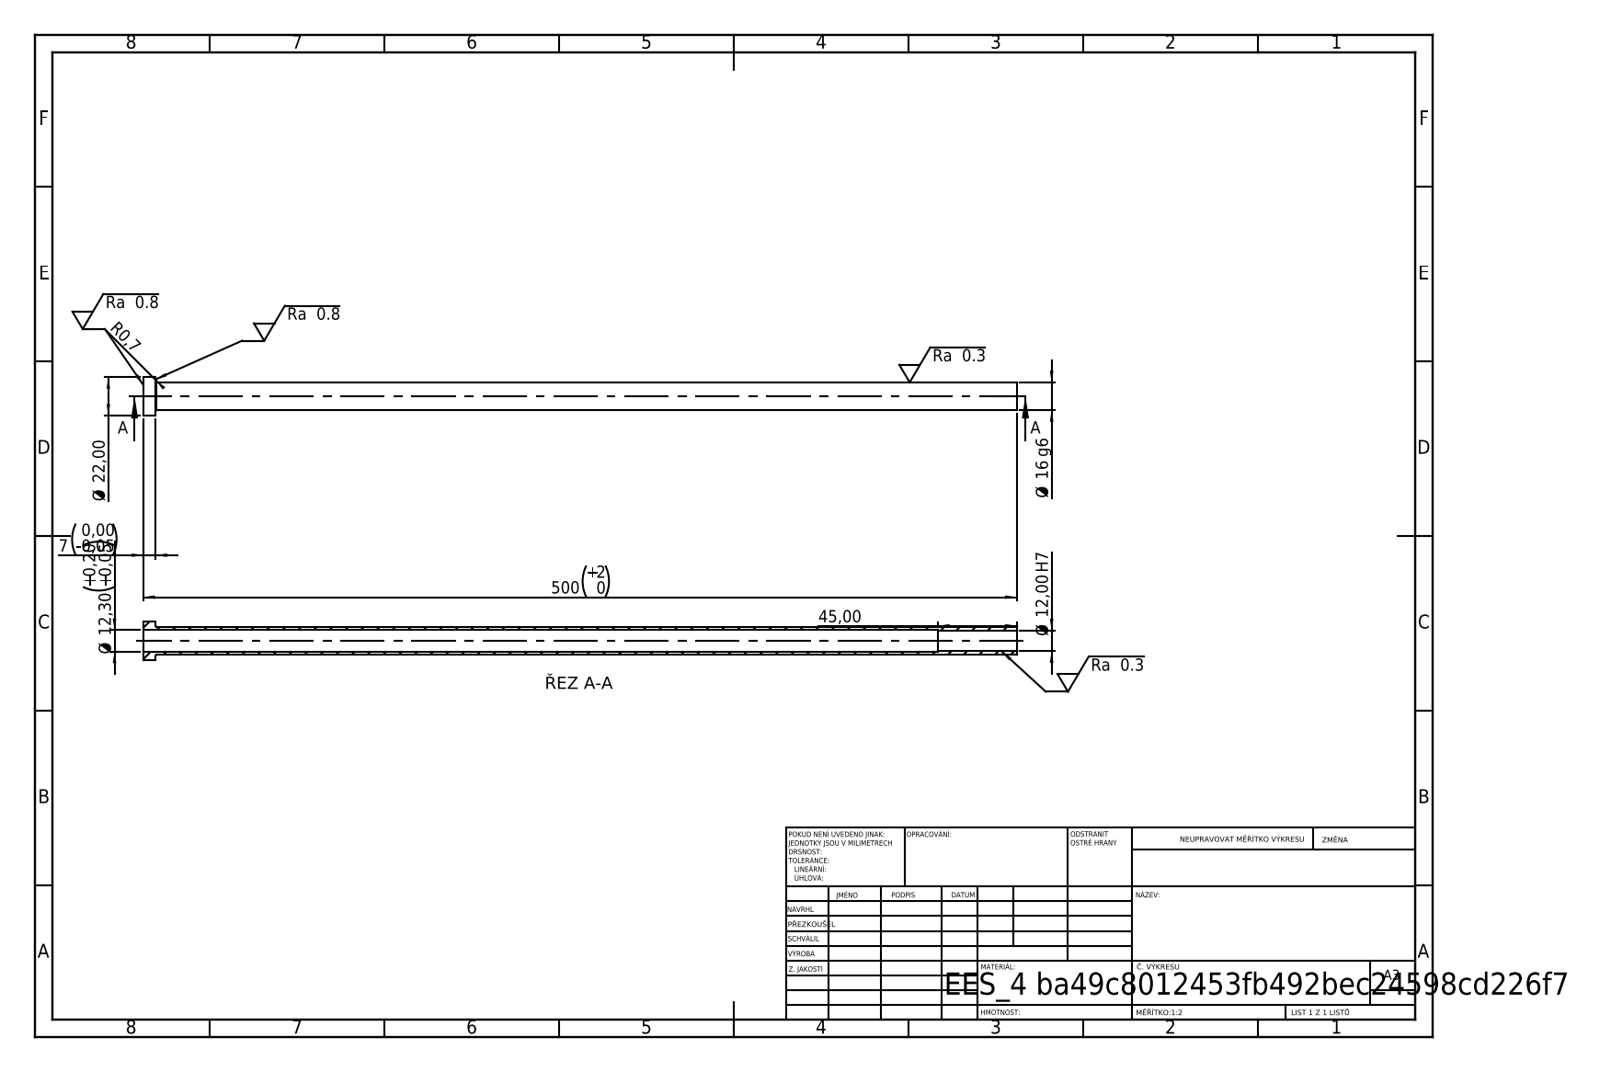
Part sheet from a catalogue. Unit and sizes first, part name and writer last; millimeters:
Units: millimetres
Overall size (bounding box): 500 × 22 × 22
Round holes (diameter × count): ⌀12 ×1, ⌀12.3 ×1
Round bosses / shafts (diameter × count): ⌀22 ×1, ⌀16 ×1
Main face-to-face distances: 7, 500, 493, 455, 448, 45
Volume: 42 636 mm³ · Surface area: 45 062 mm²
Bodies: 1 solid, 14 faces (4 planar, 8 cylindrical, 2 other)
STEP written by: SolidWorks 2019 (CONFIG_CONTROL_DESIGN)
